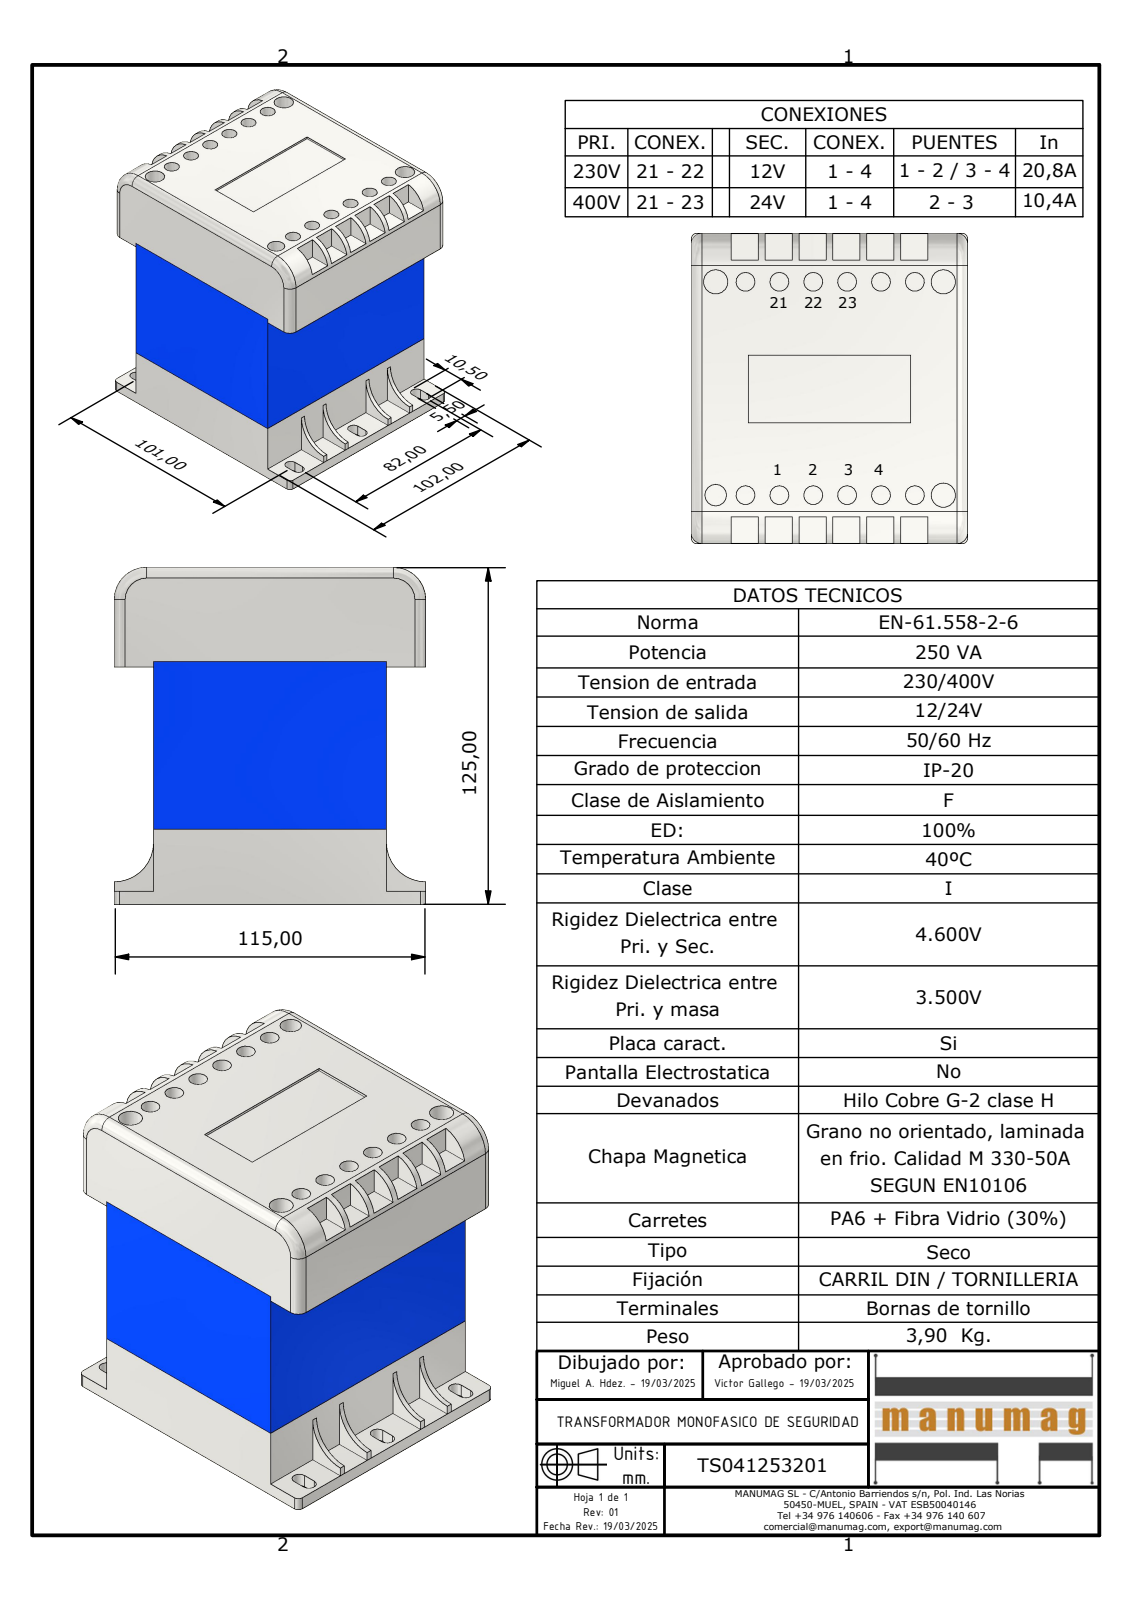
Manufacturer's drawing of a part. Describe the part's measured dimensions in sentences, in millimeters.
The part is named "TS041253201; INFERIOR EI96; CENTRAL EI96-60; SUPERIOR EI96". Its 3-D file was written by "Autodesk Inventor 2023 (AUTOMOTIVE_DESIGN)". It is 11 solids with 200 faces: 152 planar, 44 cylindrical and 4 other. Overall it measures 125 by 115 by 102 millimeters. Its volume is 483 000 cubic millimeters and its surface area 136 147 square millimeters. Round holes: 12 of diameter 7, 3 of diameter 9, 1 of diameter 8. Partial cylindrical surfaces (rounded edges, fillets, slot ends): 8 of radius 2.5, 6 of radius 4, 4 of radius 2, 2 of radius 12, 2 of radius 14.5. The main face-to-face distances are 1, 85, 101, 5, 102, 90, 86, 84, 100, 35. The hole center spacings are 12.5, 79.98, 25, 79, 82.86, 37.5, 87.45, 50.
